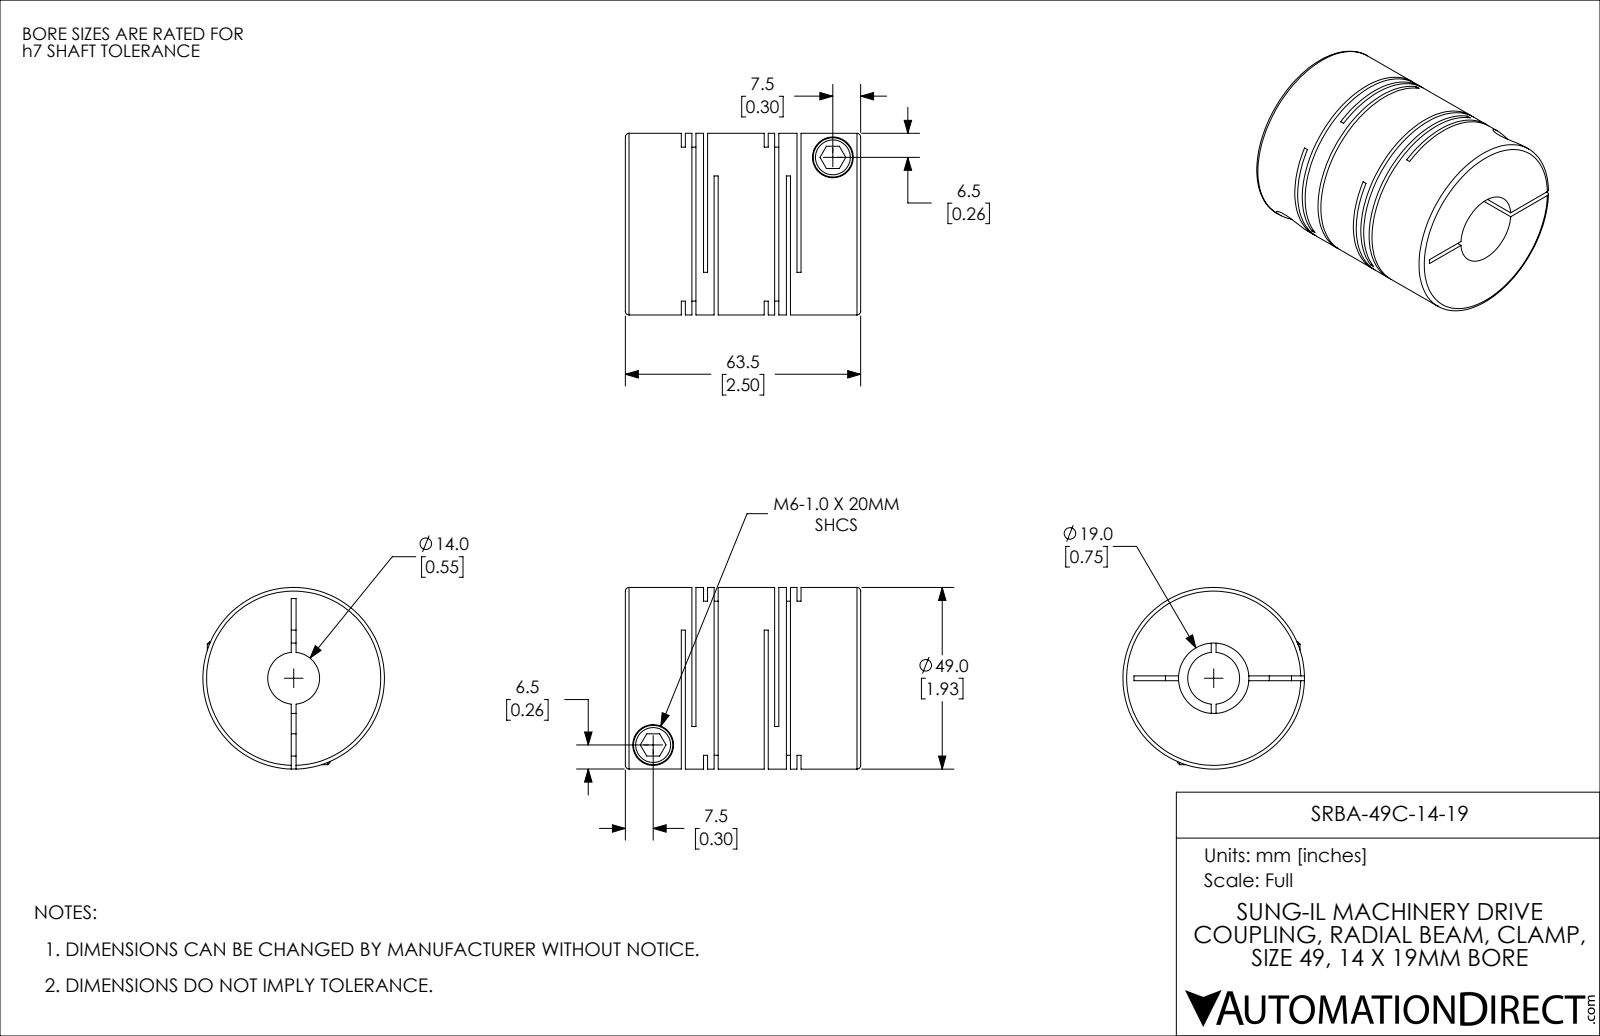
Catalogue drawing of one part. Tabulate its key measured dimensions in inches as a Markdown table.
| quantity | value |
| --- | --- |
| part name | SRBA-49C-14-19 |
| STEP written by | SolidWorks 2021 (CONFIG_CONTROL_DESIGN) |
| units | inches |
| bodies | 1 solid, 114 faces (60 planar, 42 cylindrical, 12 other) |
| overall size | 2.5 × 1.929 × 1.929 |
| volume | 5.475 in³ |
| surface area | 59.78 in² |
| round holes (diameter × count) | 0.236 × 2, 0.433 × 2, 0.551 × 1, 0.748 × 1 |
| round bosses / shafts (diameter × count) | 0.417 × 2, 1.929 × 1 |
| main face-to-face distances | 0.236, 0.043, 0.88, 0.112, 0.069, 0.193, 0.837, 0.124, 0.768, 0.644 |
